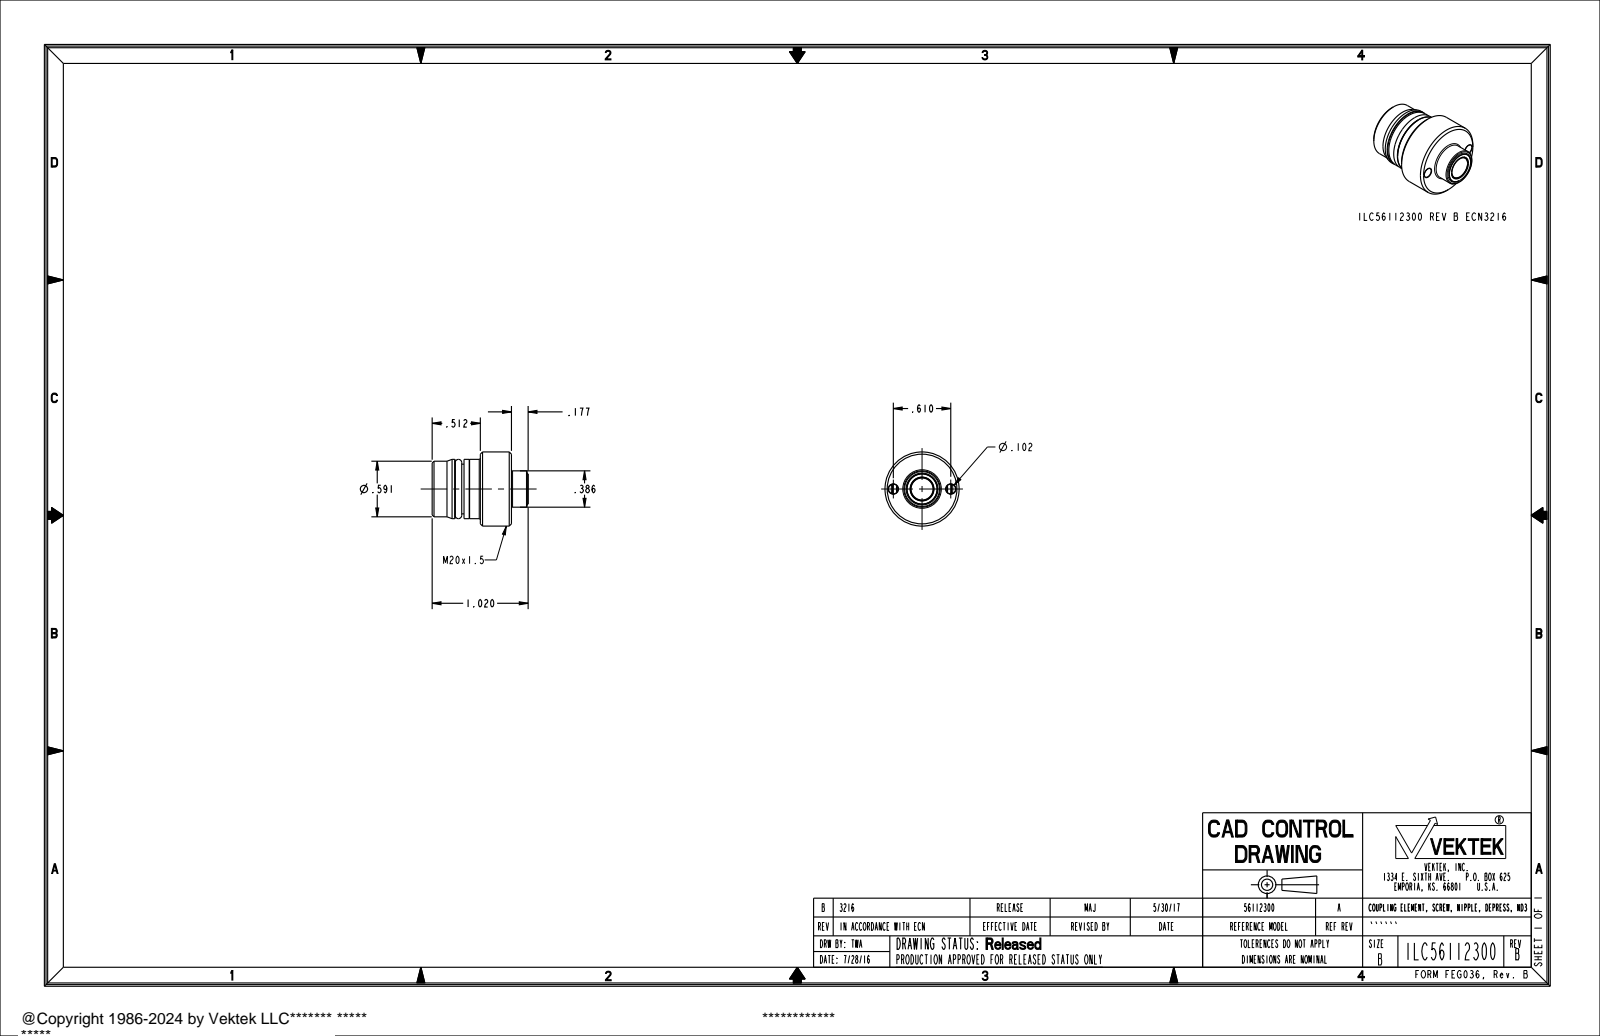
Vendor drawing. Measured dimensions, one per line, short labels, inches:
name: ILC56112300
written by: PRO/ENGINEER BY PARAMETRIC TECHNOLOGY CORPORATION, 2013320 (AUTOMOTIVE_DESIGN)
unit: in
bodies: 1 solid, 101 faces (13 planar, 52 cylindrical, 36 other)
size: 1.02 × 0.787 × 0.787
volume: 0.007 in³; area: 5.152 in²
holes: 2× ⌀0.102, 1× ⌀0.242, 1× ⌀0.248, 1× ⌀0.394, 1× ⌀0.417
bosses: 6× ⌀0.079, 2× ⌀0.047, 1× ⌀0.787, 1× ⌀0.63, 1× ⌀0.591, 1× ⌀0.528, 1× ⌀0.386
rounds: 4× R0.059, 1× R0.182
face distances: 0.843, 0.512, 0.331, 0.177, 0.776, 0.217, 0.294, 0.625, 0.394, 0.176
hole spacings: 0.305, 0.61
